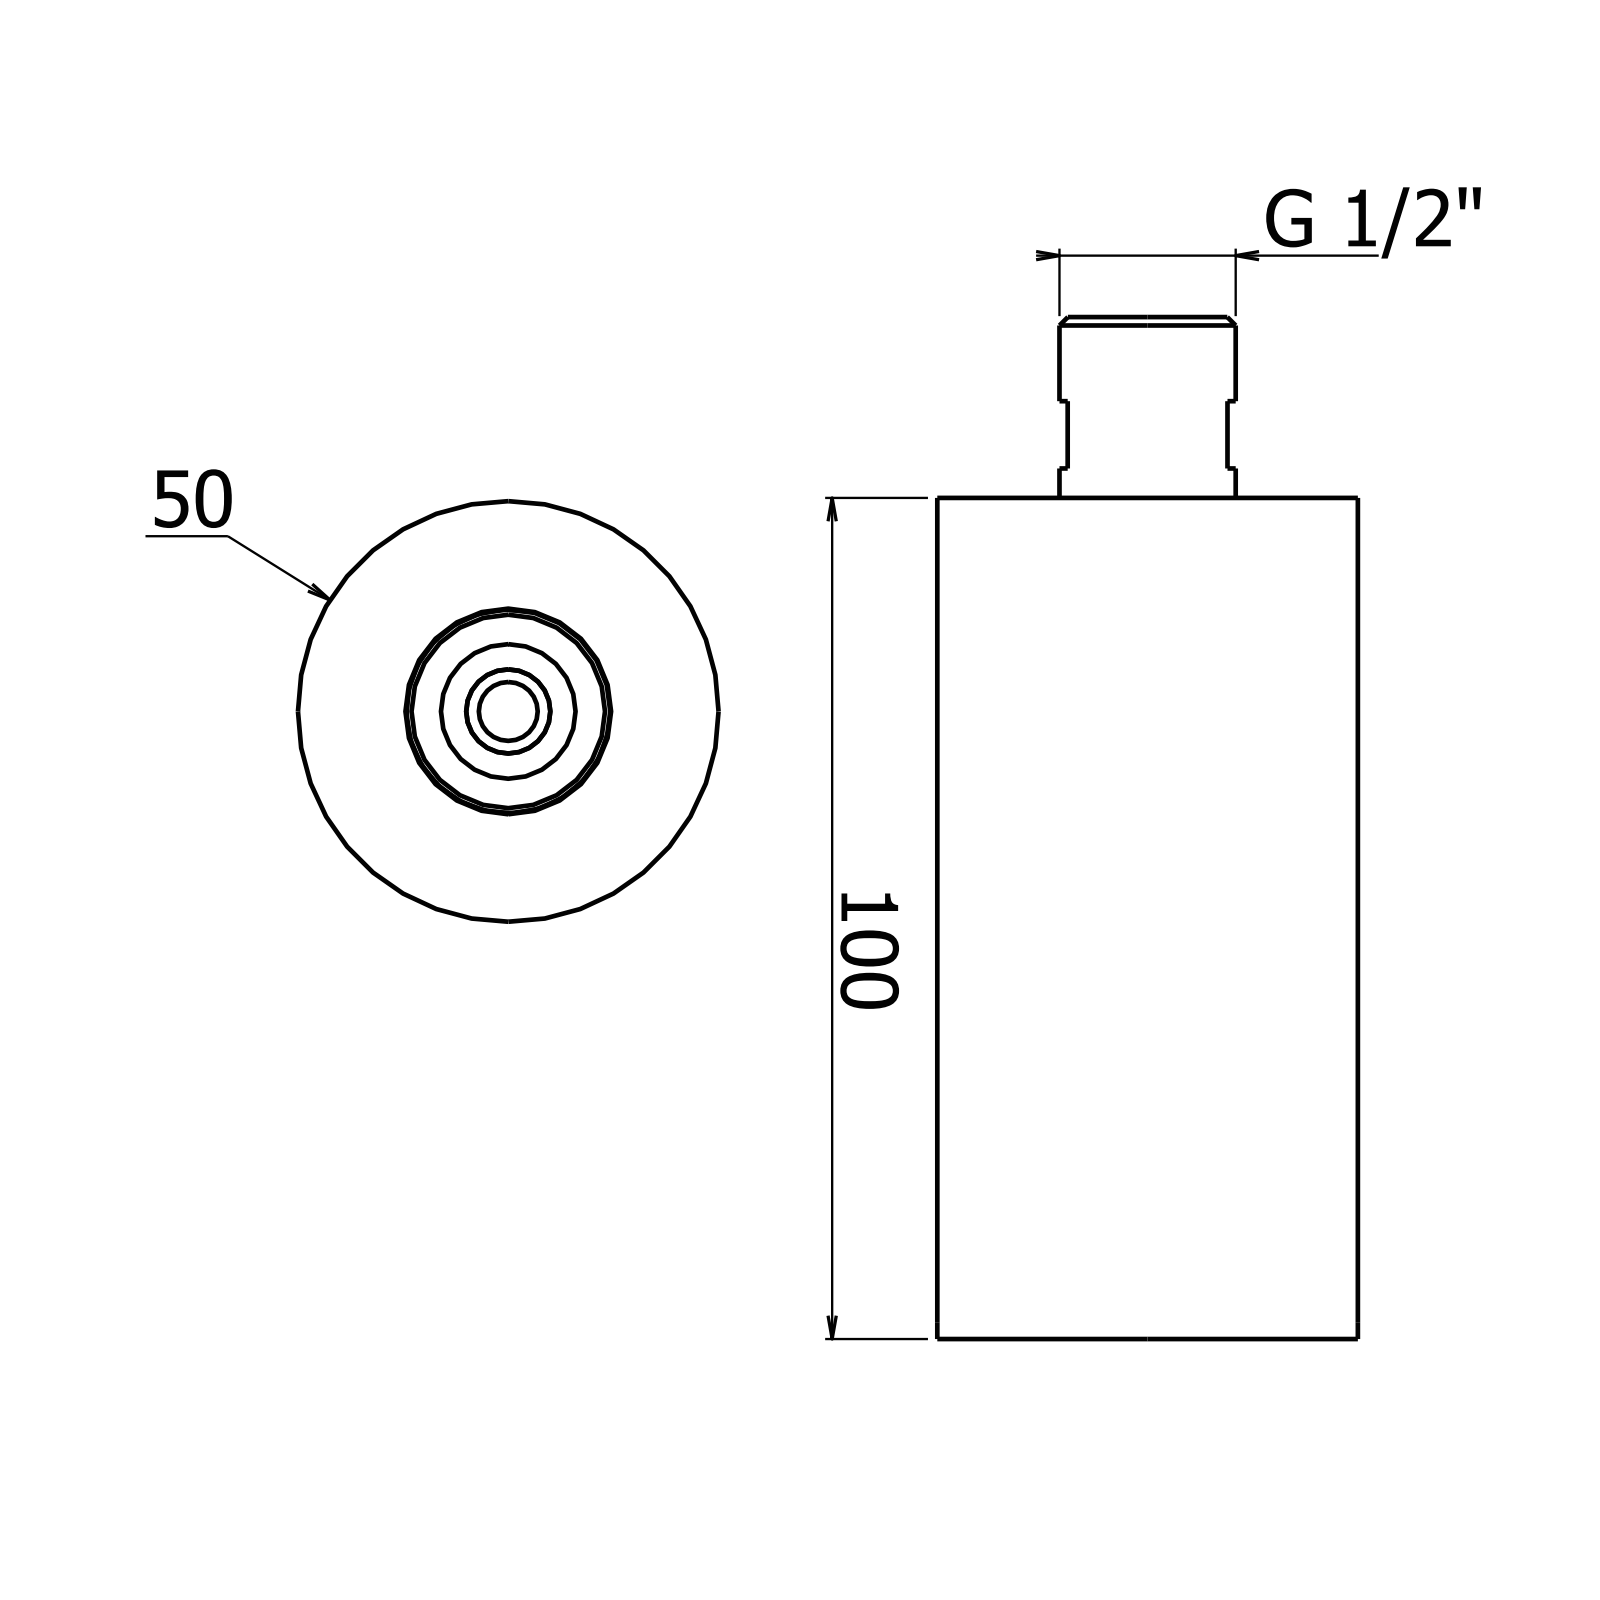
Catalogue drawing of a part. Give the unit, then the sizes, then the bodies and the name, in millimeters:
Units: millimetres
Overall size (bounding box): 122.8 × 50 × 50
Round holes (diameter × count): ⌀0.8 ×2, ⌀1.4 ×1, ⌀7 ×1, ⌀10.2 ×1, ⌀14 ×1, ⌀15 ×1, ⌀15.6 ×1, ⌀16 ×1, ⌀16.4 ×1, ⌀17.8 ×1, ⌀18.63 ×1, ⌀23 ×1
Round bosses / shafts (diameter × count): ⌀0.75 ×6, ⌀0.8 ×4, ⌀50 ×1, ⌀26 ×1, ⌀24 ×1, ⌀23.88 ×1, ⌀22.66 ×1, ⌀22.55 ×1
Partial cylindrical surfaces — rounded edges, fillets, slot ends (radius × count): R0.15 ×66, R0.25 ×66, R0.89 ×66, R0.84 ×50, R0.14 ×17, R0.14 ×15, R23.39 ×4, R24.99 ×4
Main face-to-face distances: 79, 100, 21, 1, 78, 99, 8.5, 18, 17, 61
Hole centre spacings: 4.82, 9.65
Volume: 72 681 mm³ · Surface area: 52 759 mm²
Bodies: 1 solid, 3917 faces (2826 planar, 352 cylindrical, 739 other)
Part name (STEP PRODUCT): A.R._24530/20220905
STEP written by: Spatial InterOp 3D (AUTOMOTIVE_DESIGN)
